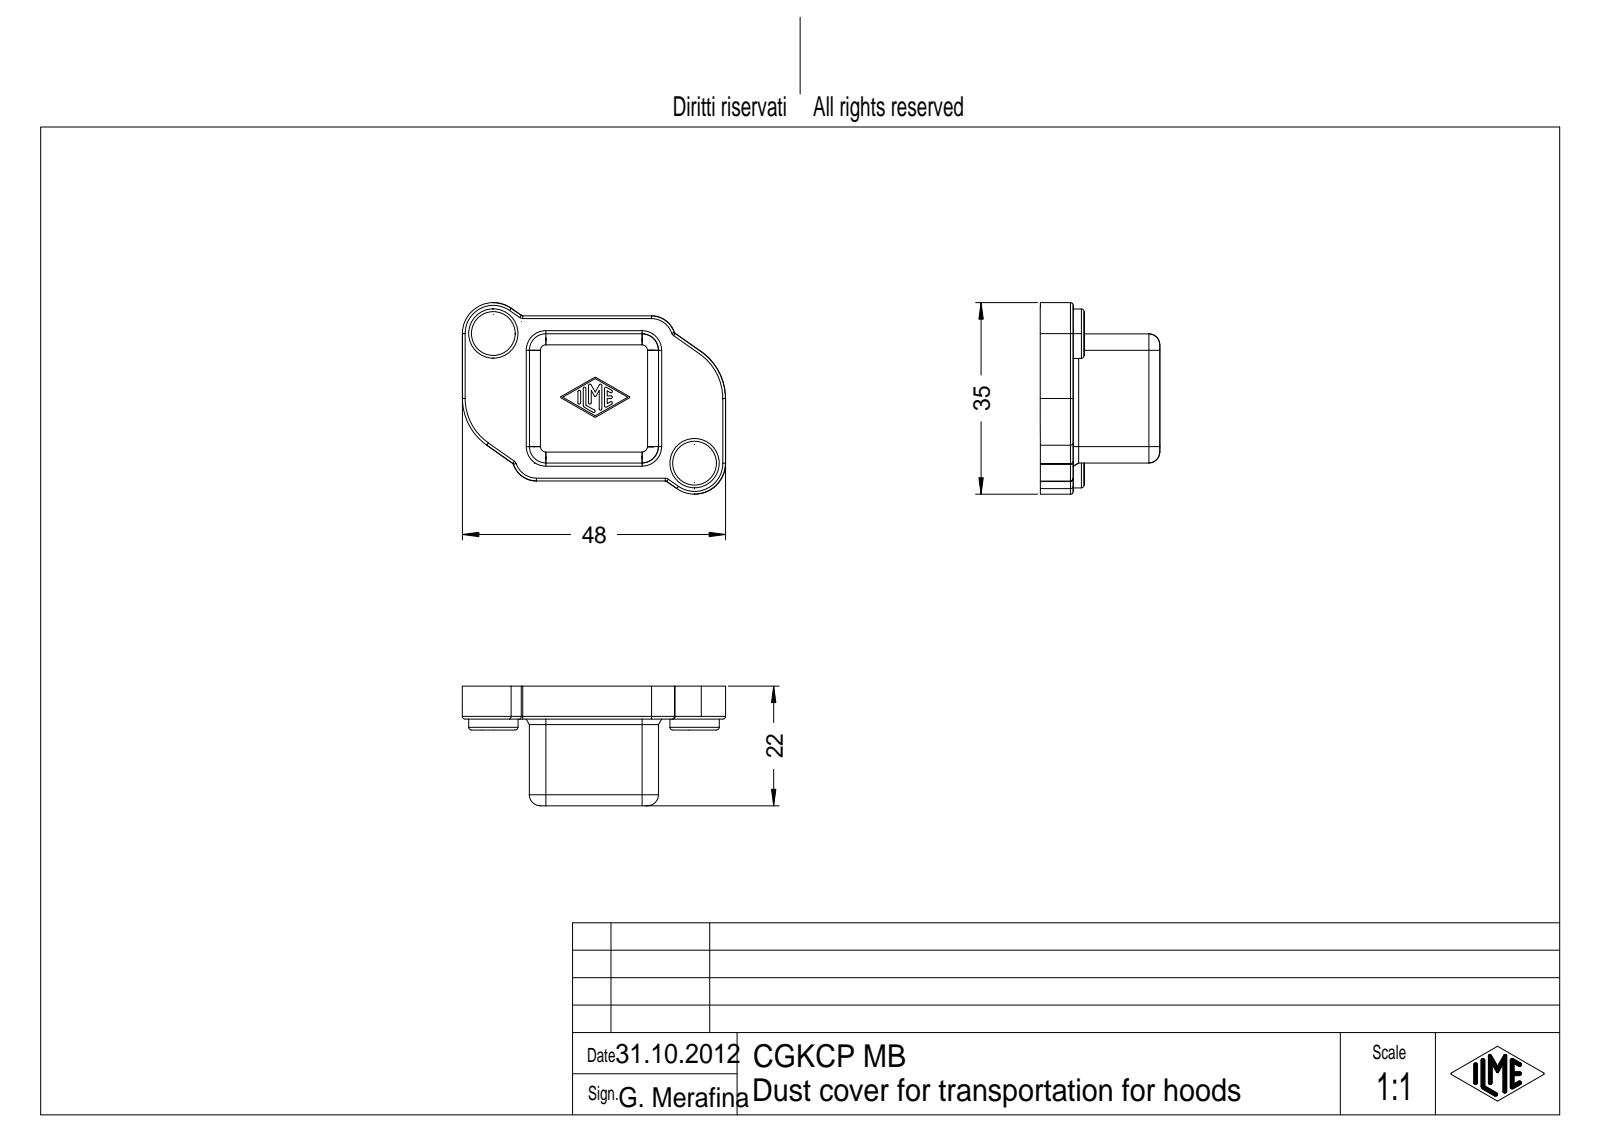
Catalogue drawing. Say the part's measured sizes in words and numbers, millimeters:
The part is named "54055". Its 3-D file was written by "Creo Elements/Direct Modeling 18.0B 02-Dec-2011 (C) Parametric Technology GmbH (AUTOMOTIVE_DESIGN)". It is 1 solid with 68 faces: 32 planar, 32 cylindrical and 4 other. Overall it measures 48 by 34.9 by 21.8 millimeters. Its volume is 10 807 cubic millimeters and its surface area 5 797 square millimeters. Round holes: 2 of diameter 7. Round bosses or shafts: 2 of diameter 9. Partial cylindrical surfaces (rounded edges, fillets, slot ends): 4 of radius 3, 2 of radius 0.3, 2 of radius 0.5, 2 of radius 0.8, 2 of radius 1.3, 2 of radius 3.4, 2 of radius 4.4, 2 of radius 4.65. The main face-to-face distances are 1, 15.8, 16.8, 23.55, 29.1, 2, 3.28, 26.83, 30.1, 26.82. The hole center spacings are 43.64.
